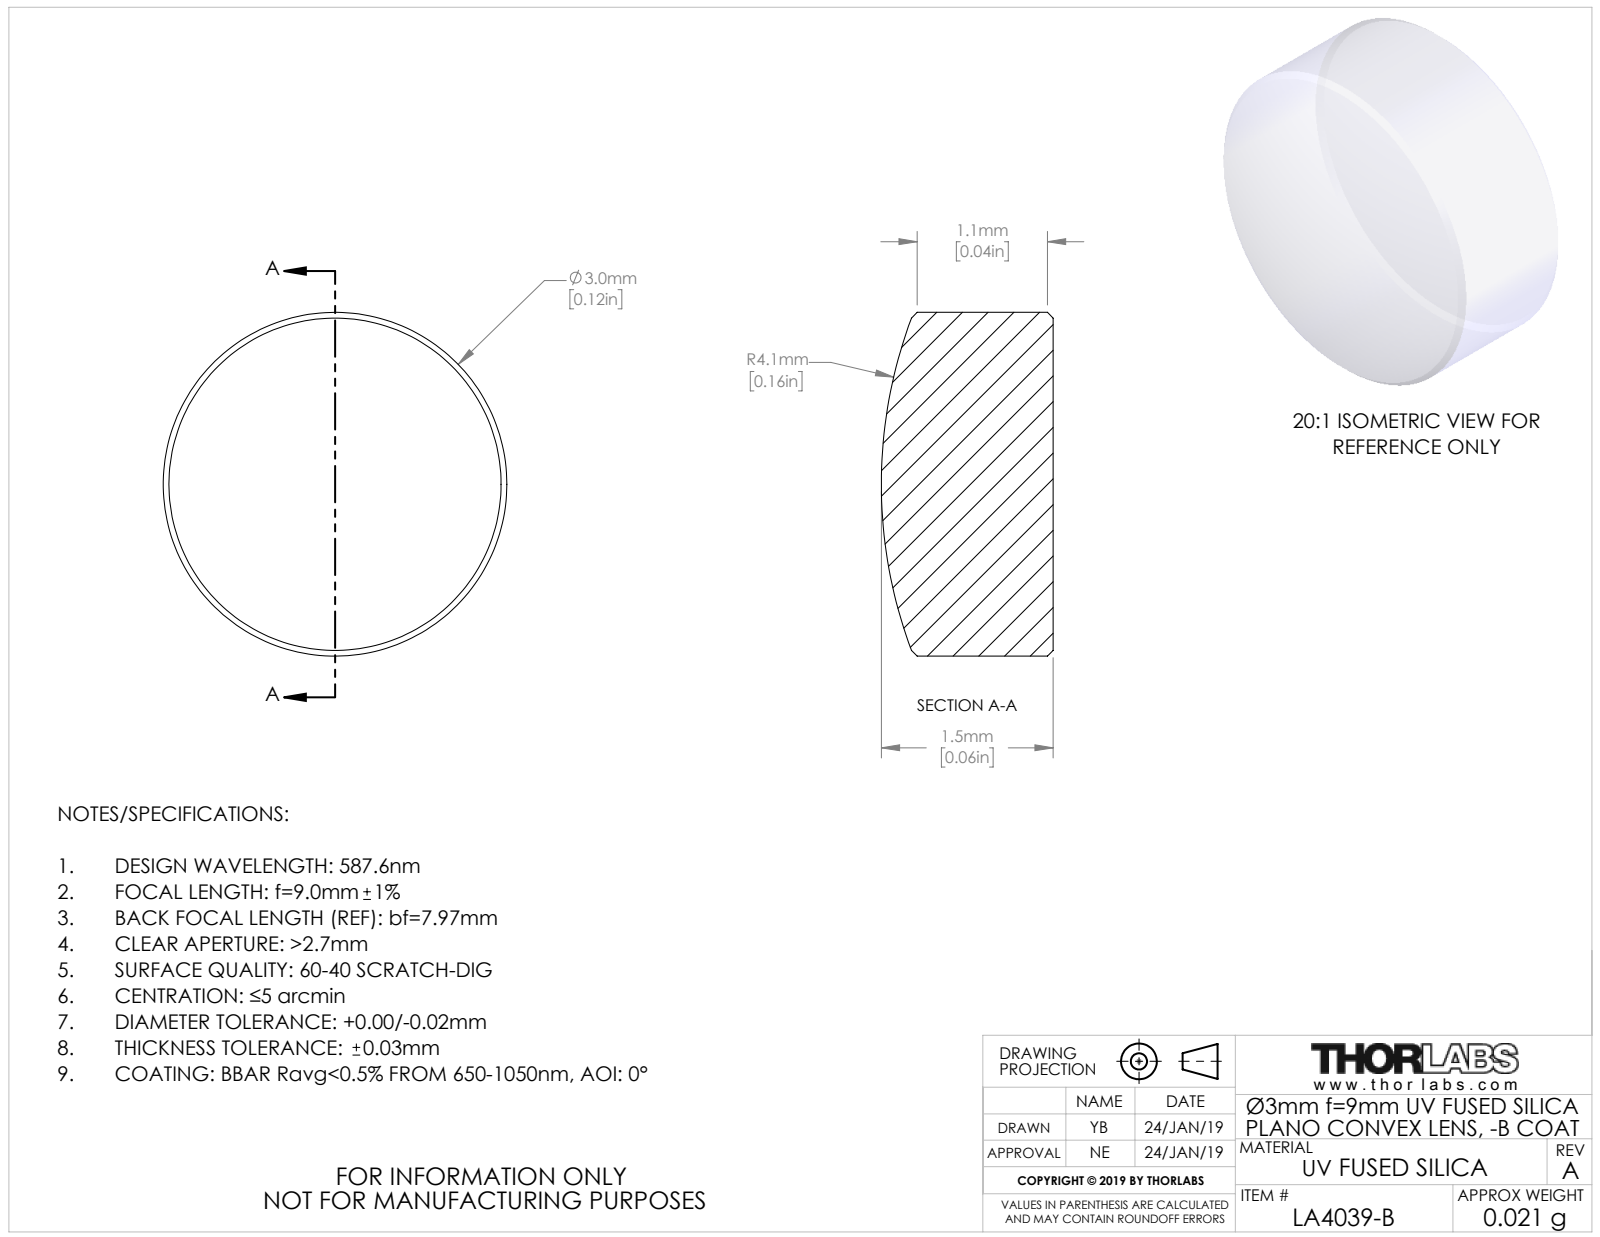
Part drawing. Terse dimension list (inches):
name: TTN162817-E0W
written by: SolidWorks 2018 (CONFIG_CONTROL_DESIGN)
unit: in
bodies: 1 solid, 9 faces (1 planar, 2 cylindrical, 6 other)
size: 0.118 × 0.118 × 0.059
volume: 0.001 in³; area: 0.039 in²
bosses: 1× ⌀0.118
